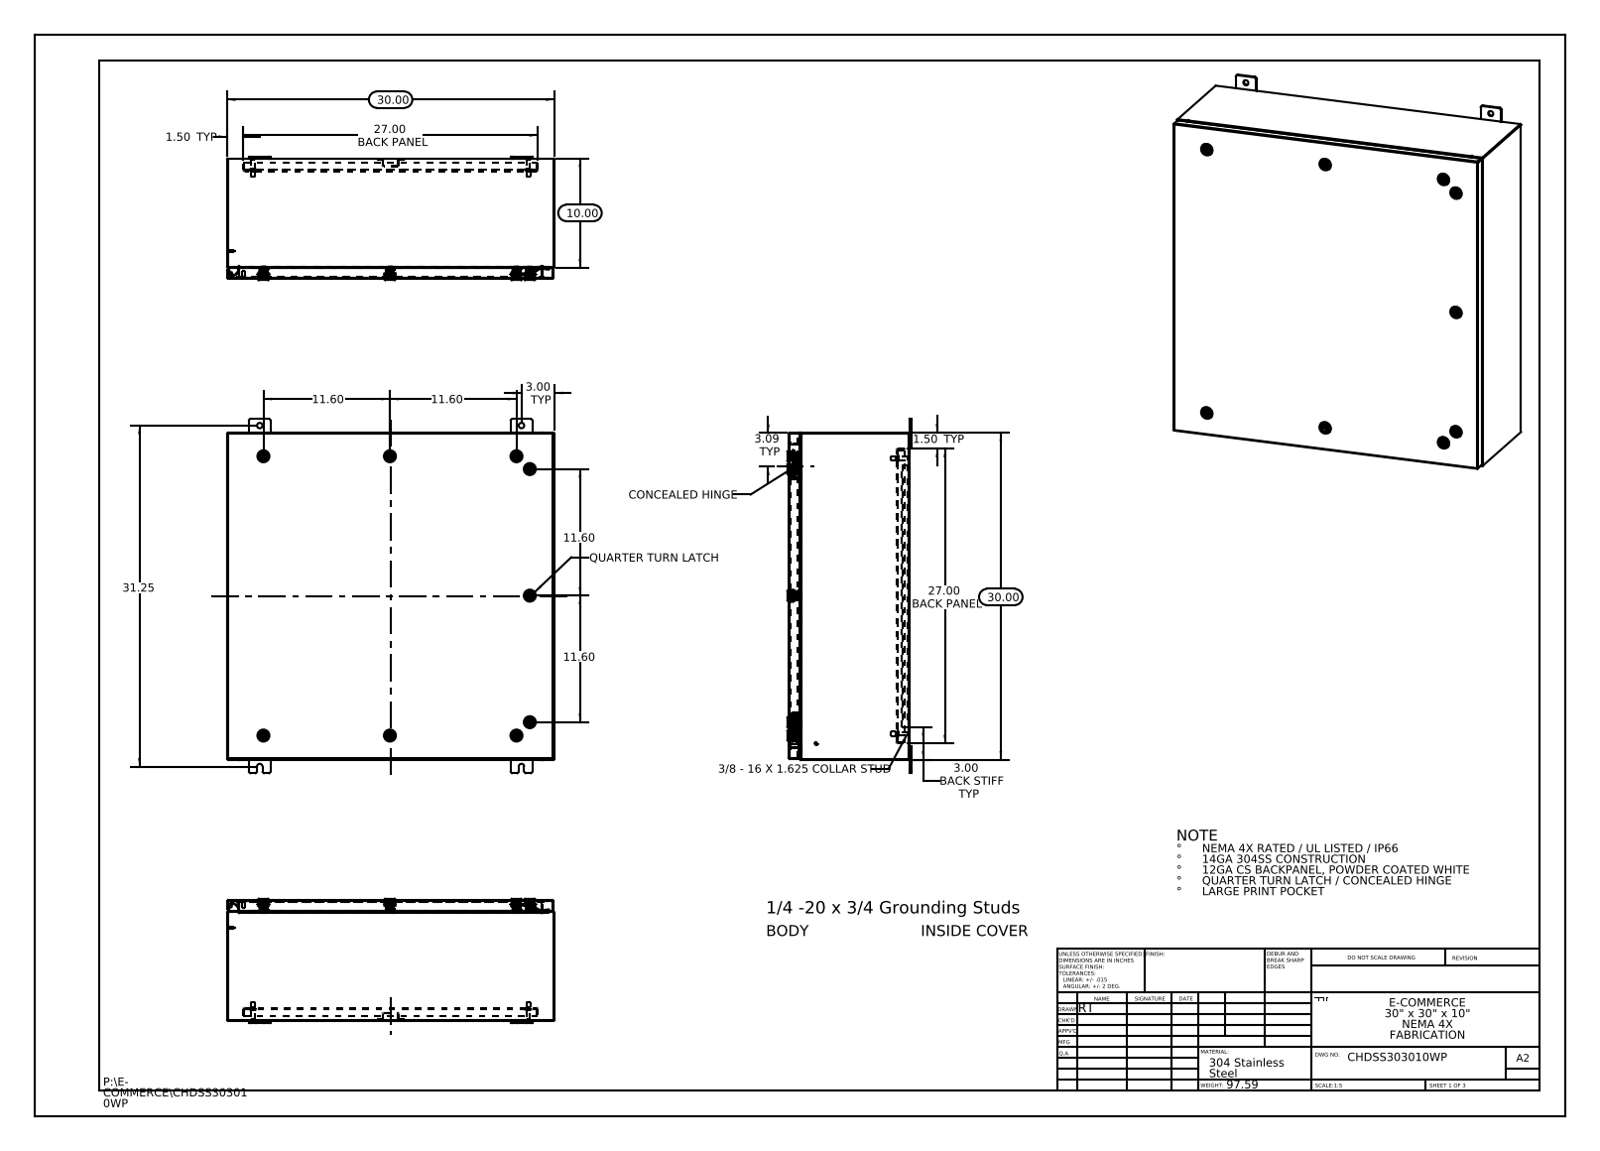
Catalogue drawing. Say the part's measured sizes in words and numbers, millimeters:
The part is named "Quarter-20 CD Stud; Screw-221320-IB-Industrilas_Screw-221320-IB-Industrilas; CHDSS303010WP Mounting Feet; Insert-221320-IB-Industrilas_Insert-221320-IB-Industrilas (+8 more)". Its 3-D file was written by "SolidWorks 2013 (CONFIG_CONTROL_DESIGN)". It is 74 solids with 7916 faces: 2280 planar, 2462 cylindrical and 3174 other. Overall it measures 825.5 by 762 by 288.4 millimeters. Its volume is 5 683 000 cubic millimeters and its surface area 5 568 000 square millimeters. Round holes: 9 of diameter 5, 9 of diameter 10, 9 of diameter 10.2, 9 of diameter 16, 9 of diameter 20, 8 of diameter 12.7, 4 of diameter 3.5, 1 of diameter 5.4. Round bosses or shafts: 11 of diameter 6, 9 of diameter 28, 9 of diameter 19.8, 9 of diameter 15.9, 9 of diameter 15.5, 9 of diameter 13.5, 9 of diameter 10, 9 of diameter 2.9. Partial cylindrical surfaces (rounded edges, fillets, slot ends): 297 of radius 0.2, 297 of radius 3, 108 of radius 0.7, 36 of radius 0.5, 36 of radius 5, 26 of radius 0.3, 24 of radius 4.8, 22 of radius 2.2. The main face-to-face distances are 1.9, 760.1, 1.9, 279.7, 277.7, 277.8, 275.9, 2.6, 25.4, 27.3. The hole center spacings are 294.6, 713.9, 589.3, 650.2, 17.5, 47.2, 327.2, 601.6.
